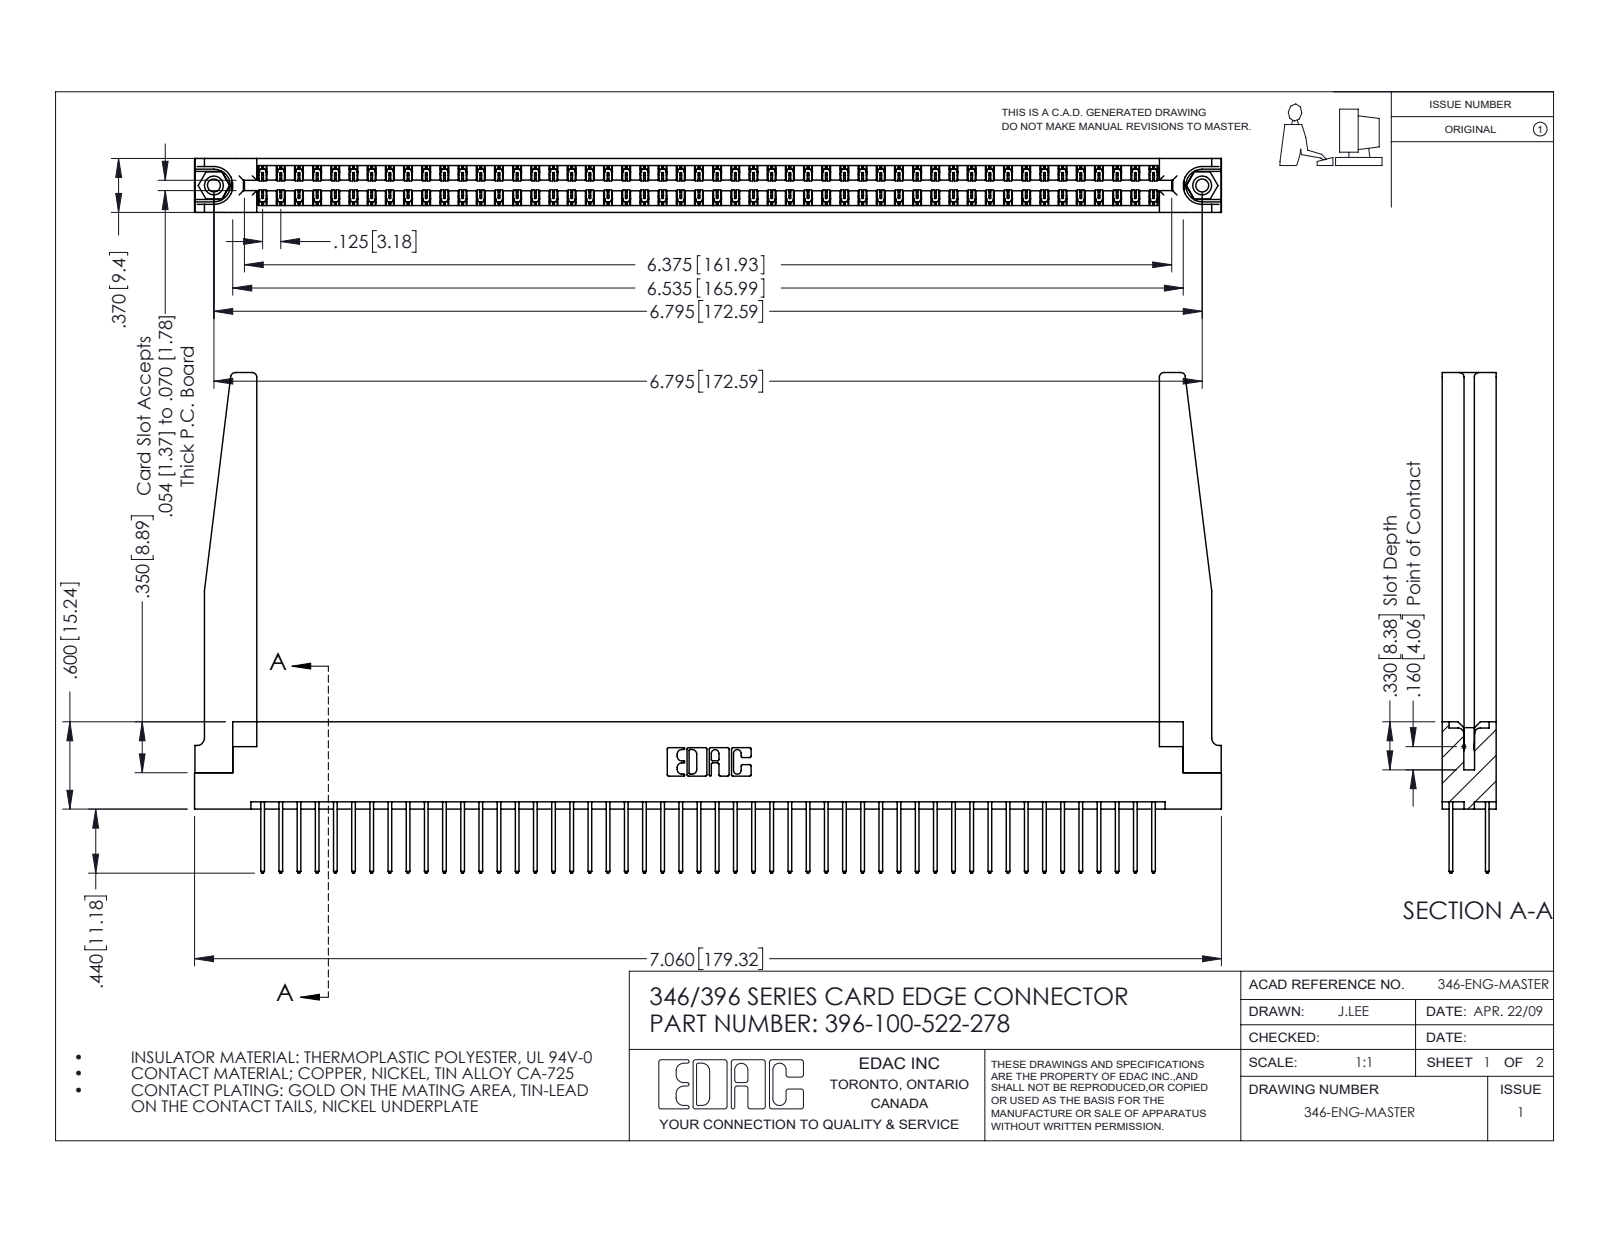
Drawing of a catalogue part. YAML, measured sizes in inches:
part_name: "345-250-001_345-250-001-102; 346-220-078_345-220-078; 396-100-522-278; 345-292-001_345-293-122 (+1 more)"
step_written_by: "SolidWorks 2016 (CONFIG_CONTROL_DESIGN)"
units: inches
bodies: {solids: 105, faces: 5556, planar: 3718, cylindrical: 1786, other: 52}
overall_size: [7.06, 3.44, 0.37]
volume: 1.508
surface_area: 50.1
round_holes:
  - {diameter: 0.089, count: 2}
  - {diameter: 0.125, count: 2}
  - {diameter: 0.156, count: 2}
  - {diameter: 0.064, count: 1}
round_bosses_or_shafts:
  - {diameter: 0.155, count: 2}
partial_cylinders:
  - {radius: 0.006, count: 150}
  - {radius: 0.01, count: 100}
  - {radius: 0.01, count: 22}
  - {radius: 0.03, count: 8}
  - {radius: 0.007, count: 6}
  - {radius: 0.031, count: 6}
  - {radius: 0.026, count: 3}
  - {radius: 0.014, count: 2}
face_to_face_distances: [0.048, 0.322, 0.37, 0.072, 0.25, 0.298, 0.025, 0.148, 0.15, 0.275]
hole_center_spacings: [0.246, 6.586, 6.795]
